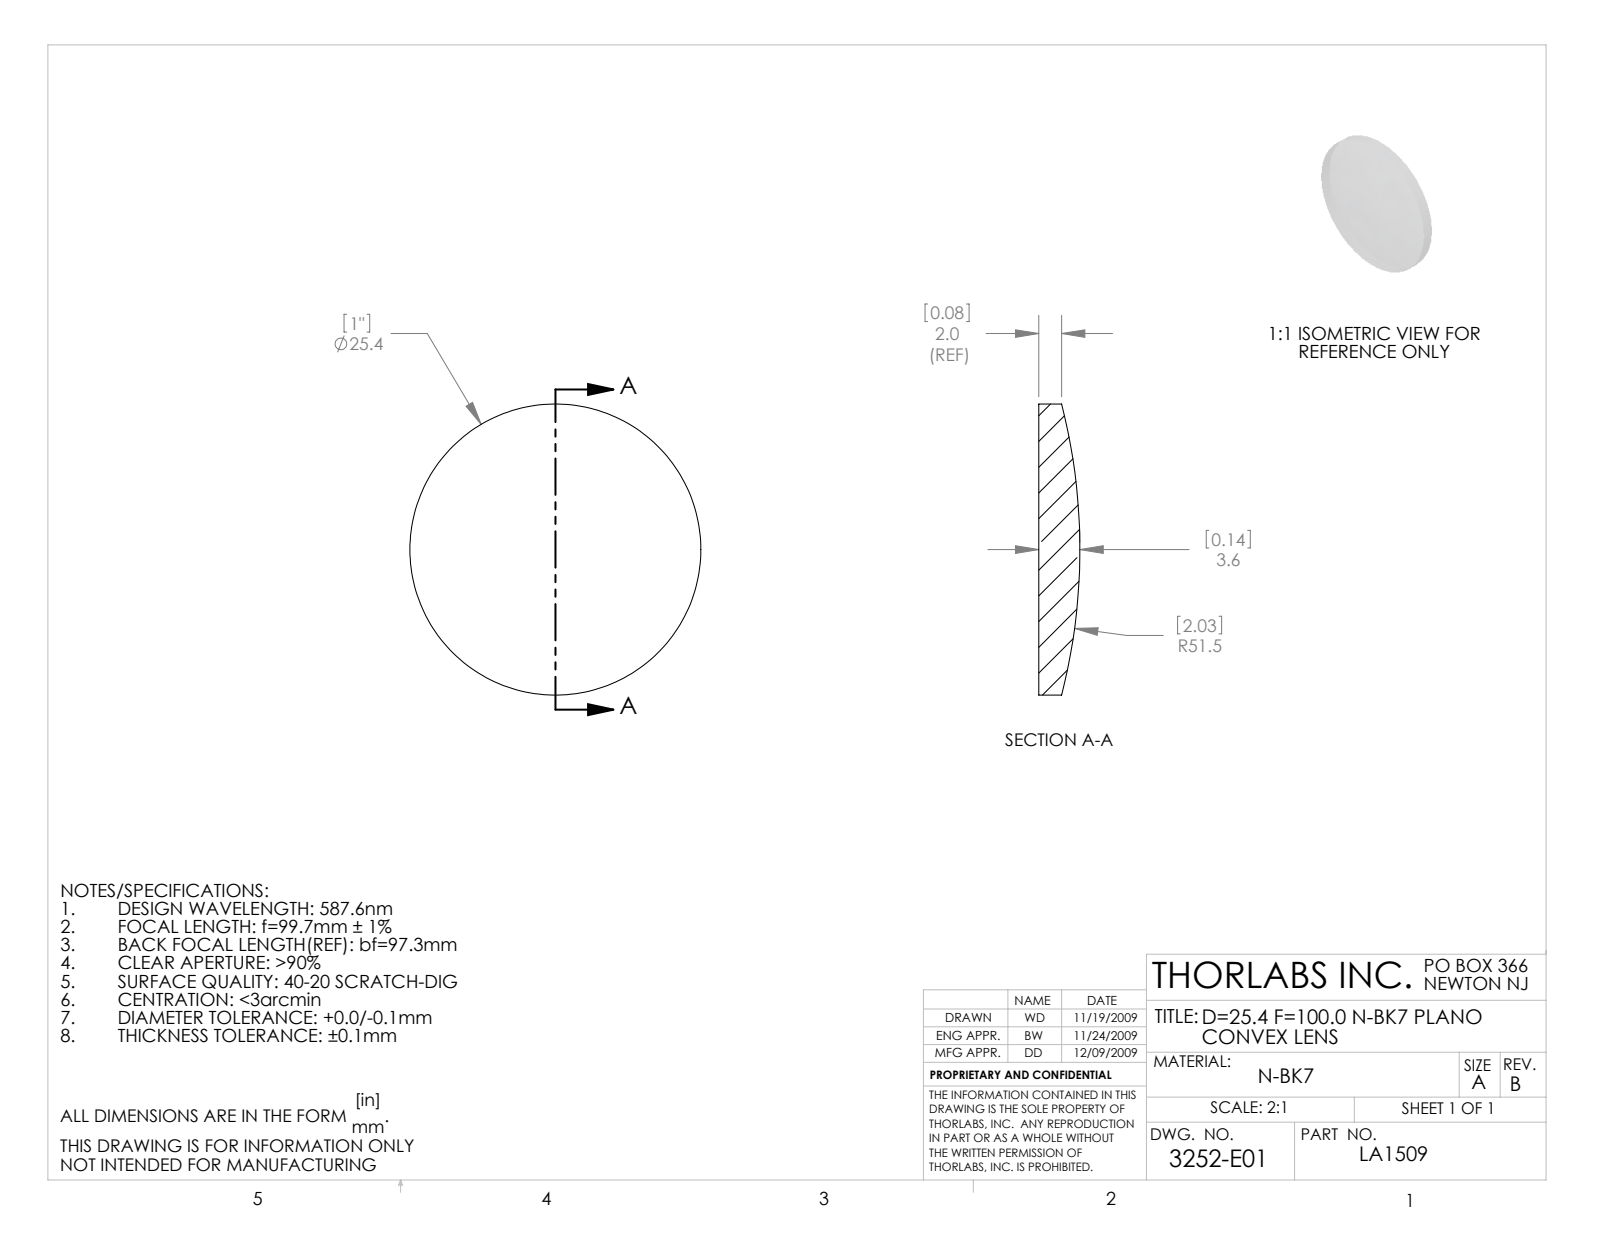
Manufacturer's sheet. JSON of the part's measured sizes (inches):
{"part_name": "3252-E0W", "step_written_by": "SolidWorks 2009 (AUTOMOTIVE_DESIGN)", "units": "inches", "bodies": {"solids": 1, "faces": 5, "planar": 1, "cylindrical": 2, "other": 2}, "overall_size": [1, 1, 0.141], "volume_in3": 0.087, "surface_area_in2": 1.831, "round_bosses_or_shafts": [[1, 1]]}
